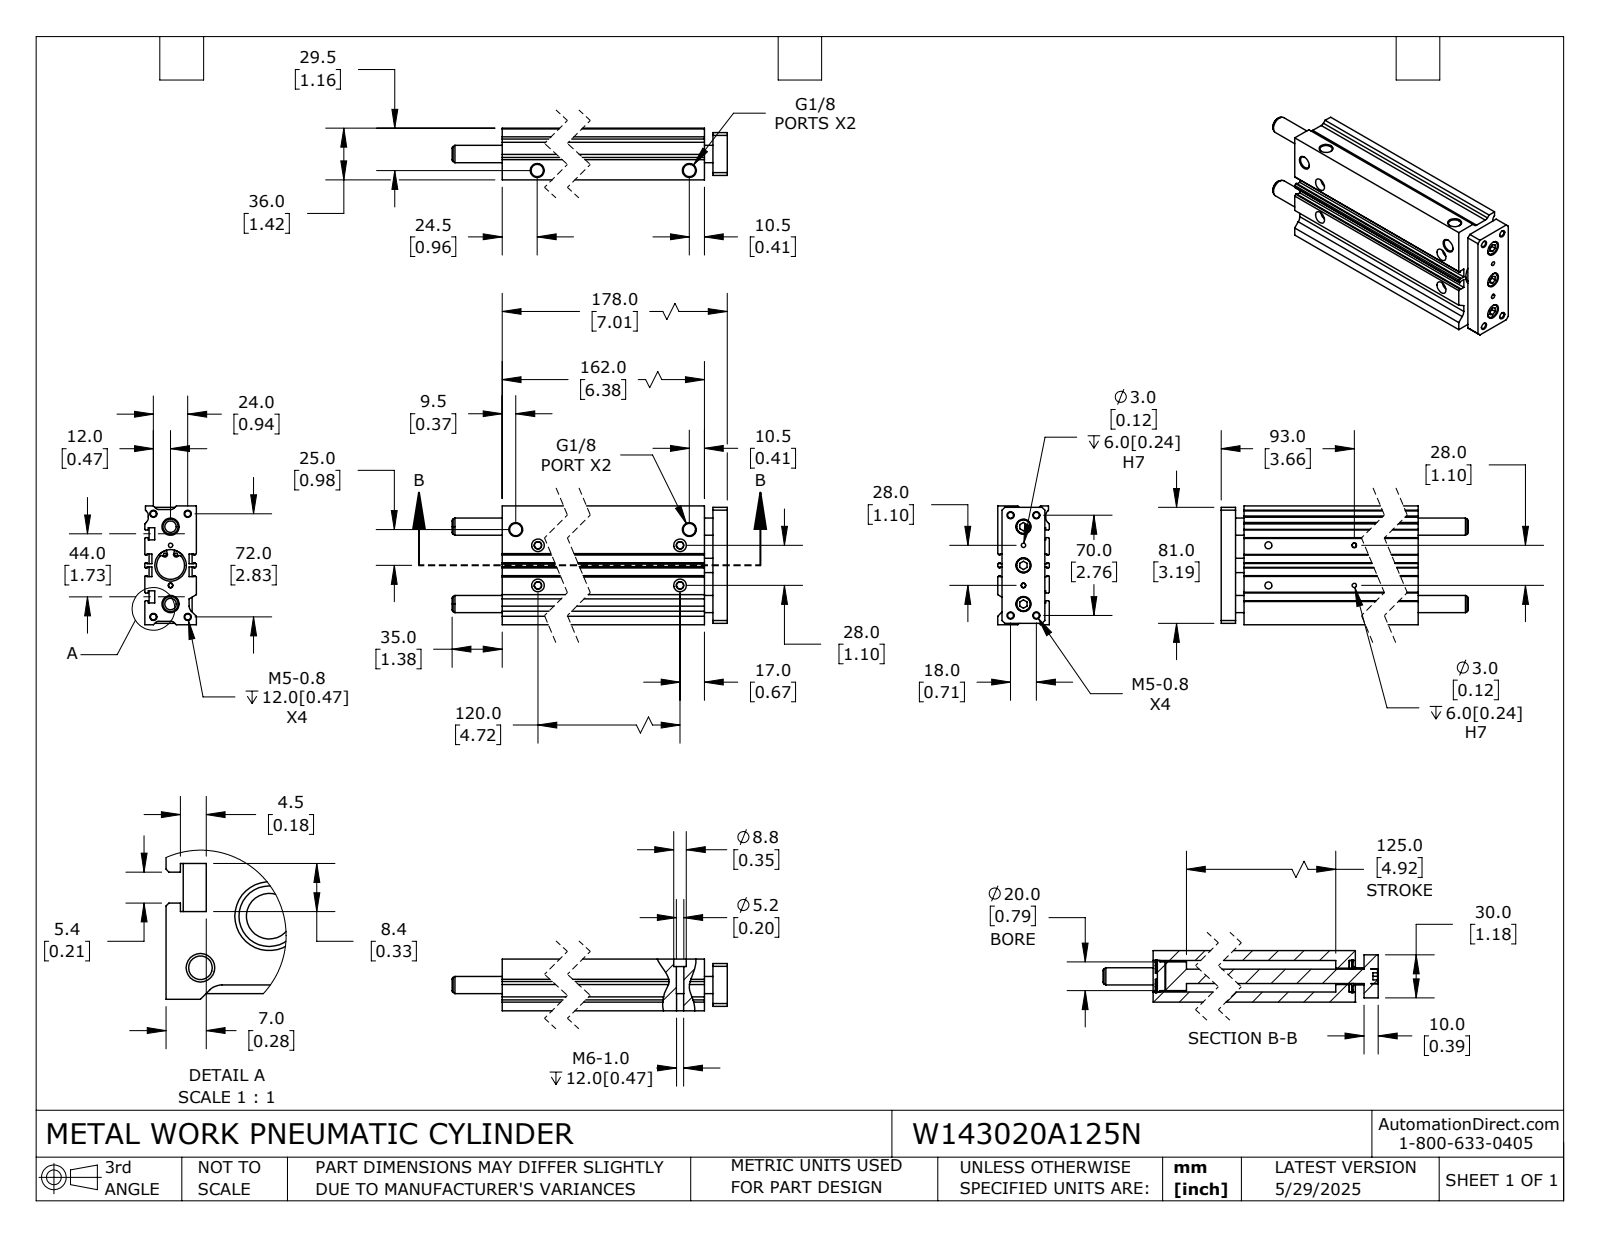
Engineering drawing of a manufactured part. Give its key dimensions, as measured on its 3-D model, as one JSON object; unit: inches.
{"part_name": "W143020A125N; W143020A125N_BODY; W143020A125N_ROD", "step_written_by": "SolidWorks 2024 (CONFIG_CONTROL_DESIGN)", "units": "inches", "bodies": {"solids": 6, "faces": 357, "planar": 174, "cylindrical": 145, "other": 38}, "overall_size": [8.386, 3.268, 1.417], "volume_in3": 25, "surface_area_in2": 183.5, "round_holes": [[0.163, 8], [0.079, 4], [0.118, 4], [0.205, 4], [0.337, 4], [0.346, 4], [0.413, 3], [0.194, 2], [0.194, 2], [0.472, 2], [0.449, 1], [0.767, 1]], "round_bosses_or_shafts": [[0.394, 3], [0.906, 2], [0.787, 1], [0.512, 1]], "partial_cylinders_radius": [[0.053, 4], [0.059, 4], [0.071, 4], [0.118, 4], [0.197, 3]], "face_to_face_distances": [1.417, 0.098, 0.197, 1.22, 0.079, 3.268, 1.024, 0.276, 3.169, 0.945], "hole_center_spacings": [0.124, 0.296, 0.336, 0.474, 0.591, 0.78, 0.828, 0.864]}
